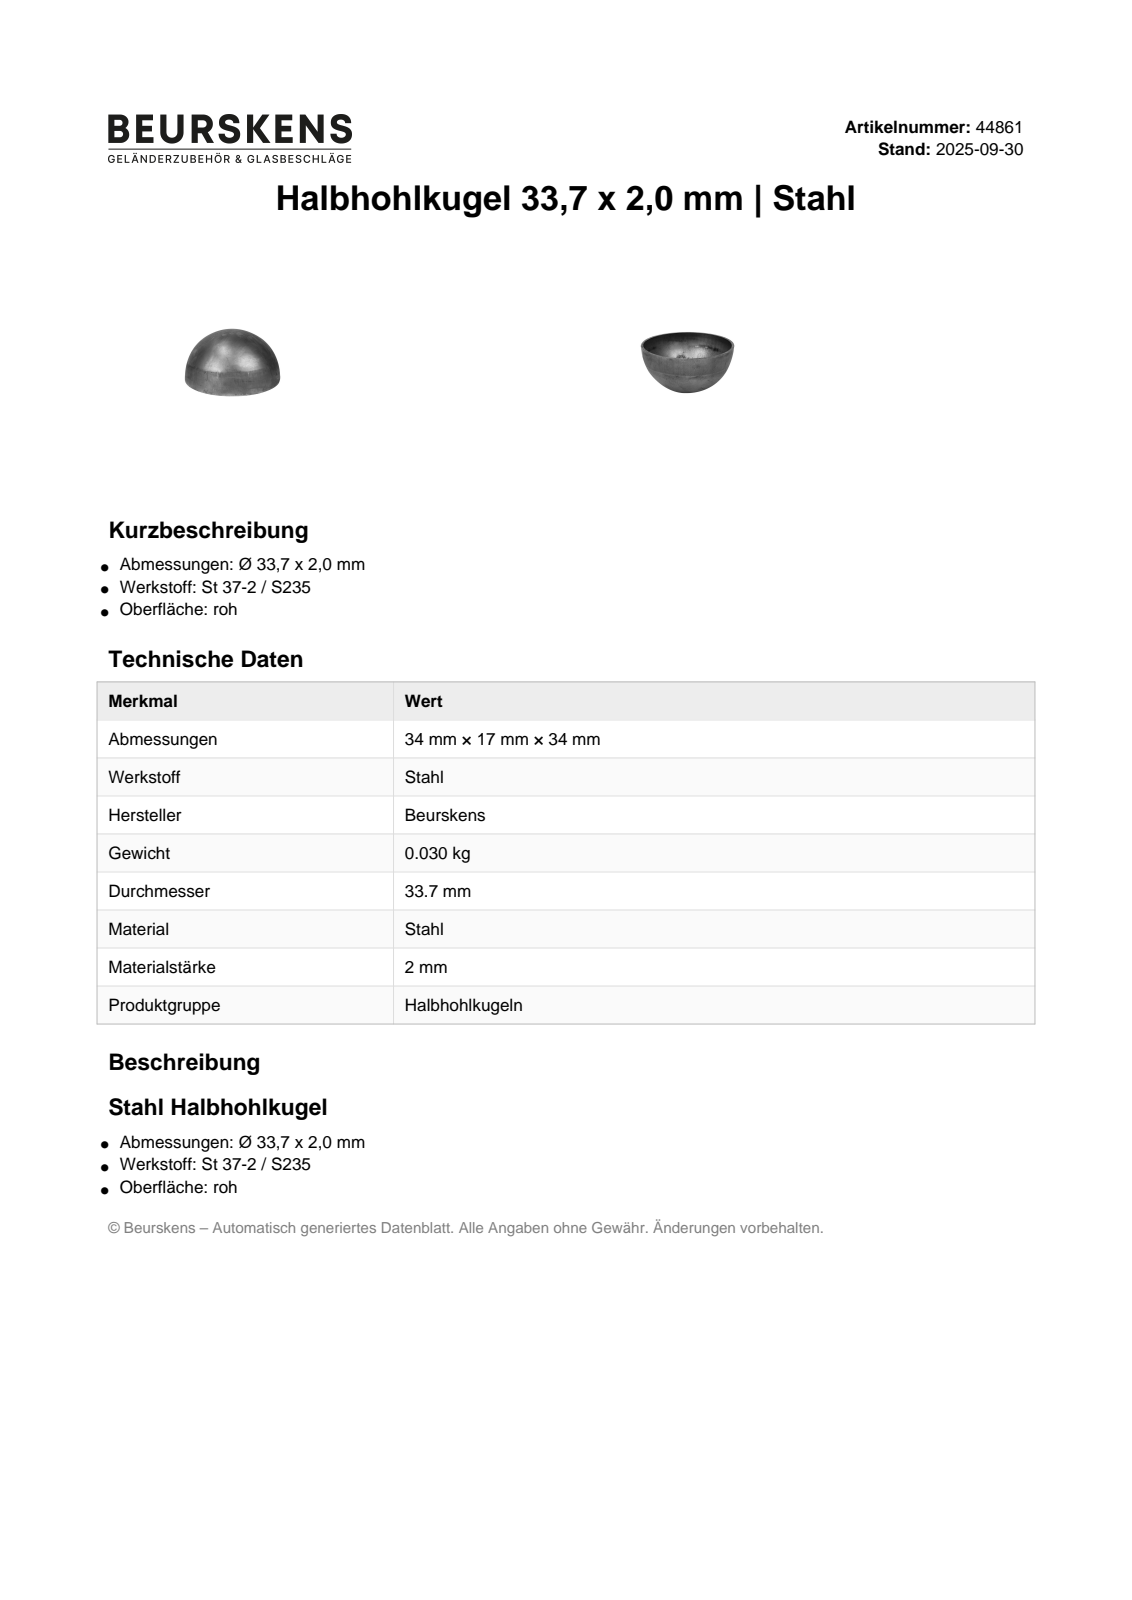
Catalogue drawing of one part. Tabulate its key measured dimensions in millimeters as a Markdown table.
| quantity | value |
| --- | --- |
| part name | 44861 |
| STEP written by | Autodesk Inventor 2023 (AUTOMOTIVE_DESIGN) |
| units | millimeters |
| bodies | 1 solid, 3 faces (1 planar, 0 cylindrical, 2 other) |
| overall size | 33.7 × 33.7 × 16.85 |
| volume | 3 161 mm³ |
| surface area | 3 369 mm² |
